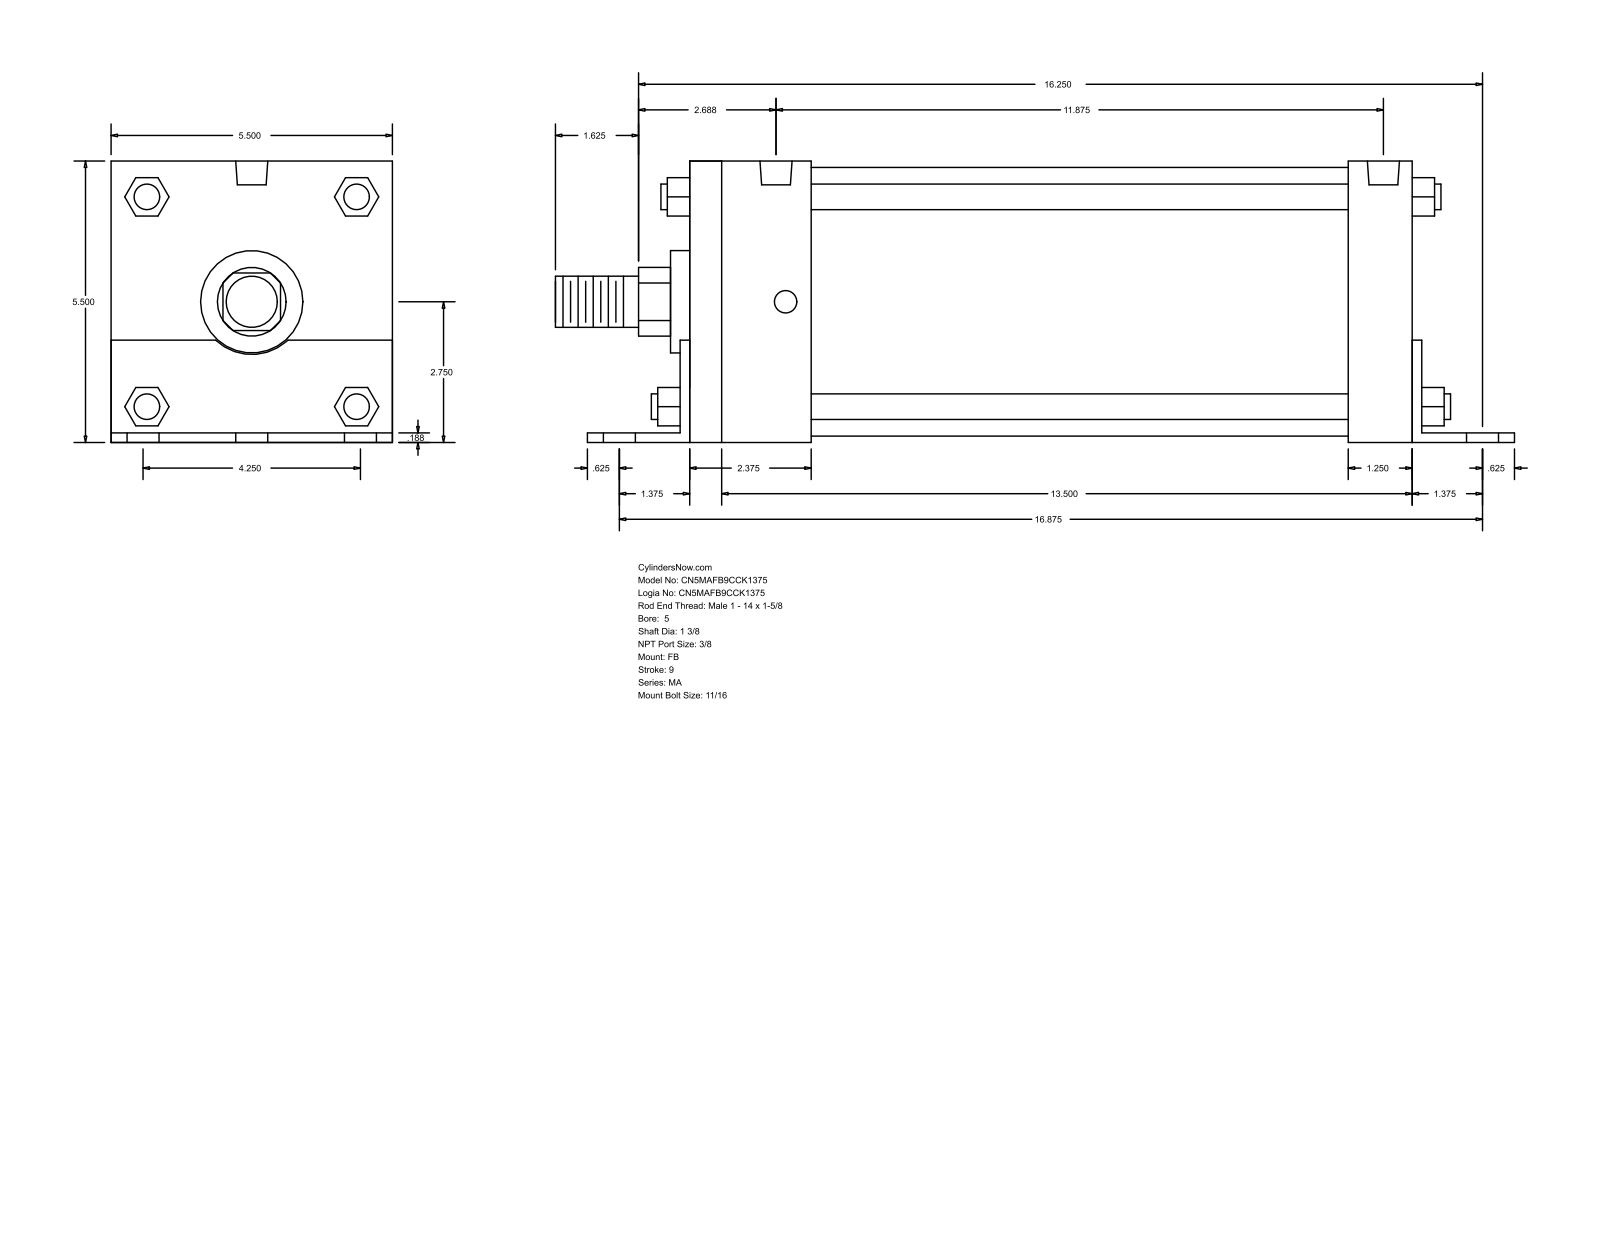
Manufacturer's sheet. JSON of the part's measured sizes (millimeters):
{"part_name": "MA_FB__0500_1.375", "step_written_by": "GSSL Pune (CONFIG_CONTROL_DESIGN)", "units": "millimeters", "bodies": {"solids": 0, "faces": 140, "planar": 105, "cylindrical": 35, "other": 0}, "overall_size": [476.25, 139.75, 139.7], "round_holes": [[17.46, 6], [11.11, 4], [15.93, 2]], "round_bosses_or_shafts": [[12.7, 4], [133.35, 1], [50.8, 1], [34.92, 1], [25.4, 1]], "partial_cylinders_radius": [[17.06, 1], [26.16, 1]], "face_to_face_distances": [139.7, 4.76, 139.75, 363.54, 4.71, 134.99, 358.78, 368.3, 31.75, 36.51], "hole_center_spacings": [53.98, 432.02, 428.63, 4.77, 73.04, 76.34, 94.68, 98.64]}
